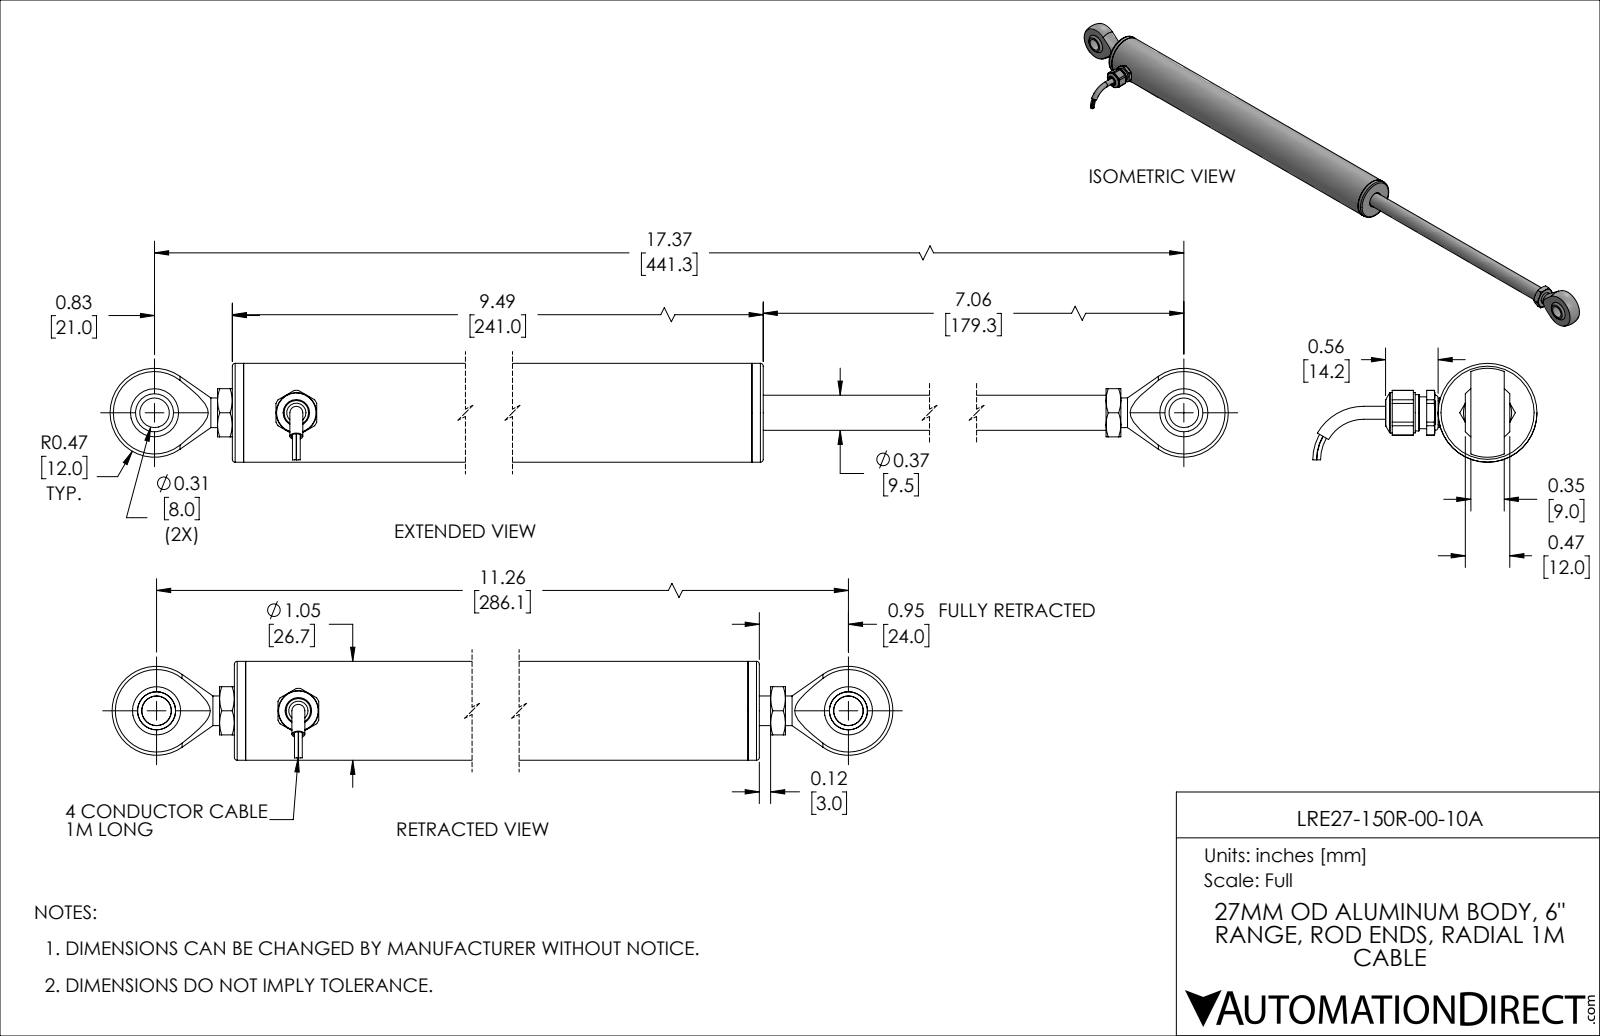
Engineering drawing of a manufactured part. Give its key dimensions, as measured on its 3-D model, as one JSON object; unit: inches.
{"part_name": "LRE27-150R-00-10A", "step_written_by": "SolidWorks 2019 (AUTOMOTIVE_DESIGN)", "units": "inches", "bodies": {"solids": 25, "faces": 285, "planar": 108, "cylindrical": 83, "other": 94}, "overall_size": [12.088, 2.382, 1.05], "volume_in3": 5.357, "surface_area_in2": 110.4, "round_holes": [[0.268, 2], [0.315, 2], [0.106, 1], [0.138, 1], [0.156, 1], [0.187, 1], [0.201, 1], [0.205, 1], [0.25, 1], [0.274, 1], [0.313, 1], [0.36, 1]], "round_bosses_or_shafts": [[0.039, 4], [0.315, 2], [1.05, 1], [0.85, 1], [0.848, 1], [0.687, 1], [0.685, 1], [0.625, 1]], "partial_cylinders_radius": [[0.01, 2], [0.067, 2], [0.25, 2], [0.197, 1], [0.224, 1], [0.238, 1]], "face_to_face_distances": [0.12, 9.37, 0.354, 9.49, 0.862, 8.628, 7.161, 1.65, 0.788, 7.84], "hole_center_spacings": [1.507, 9.637, 11.144]}
